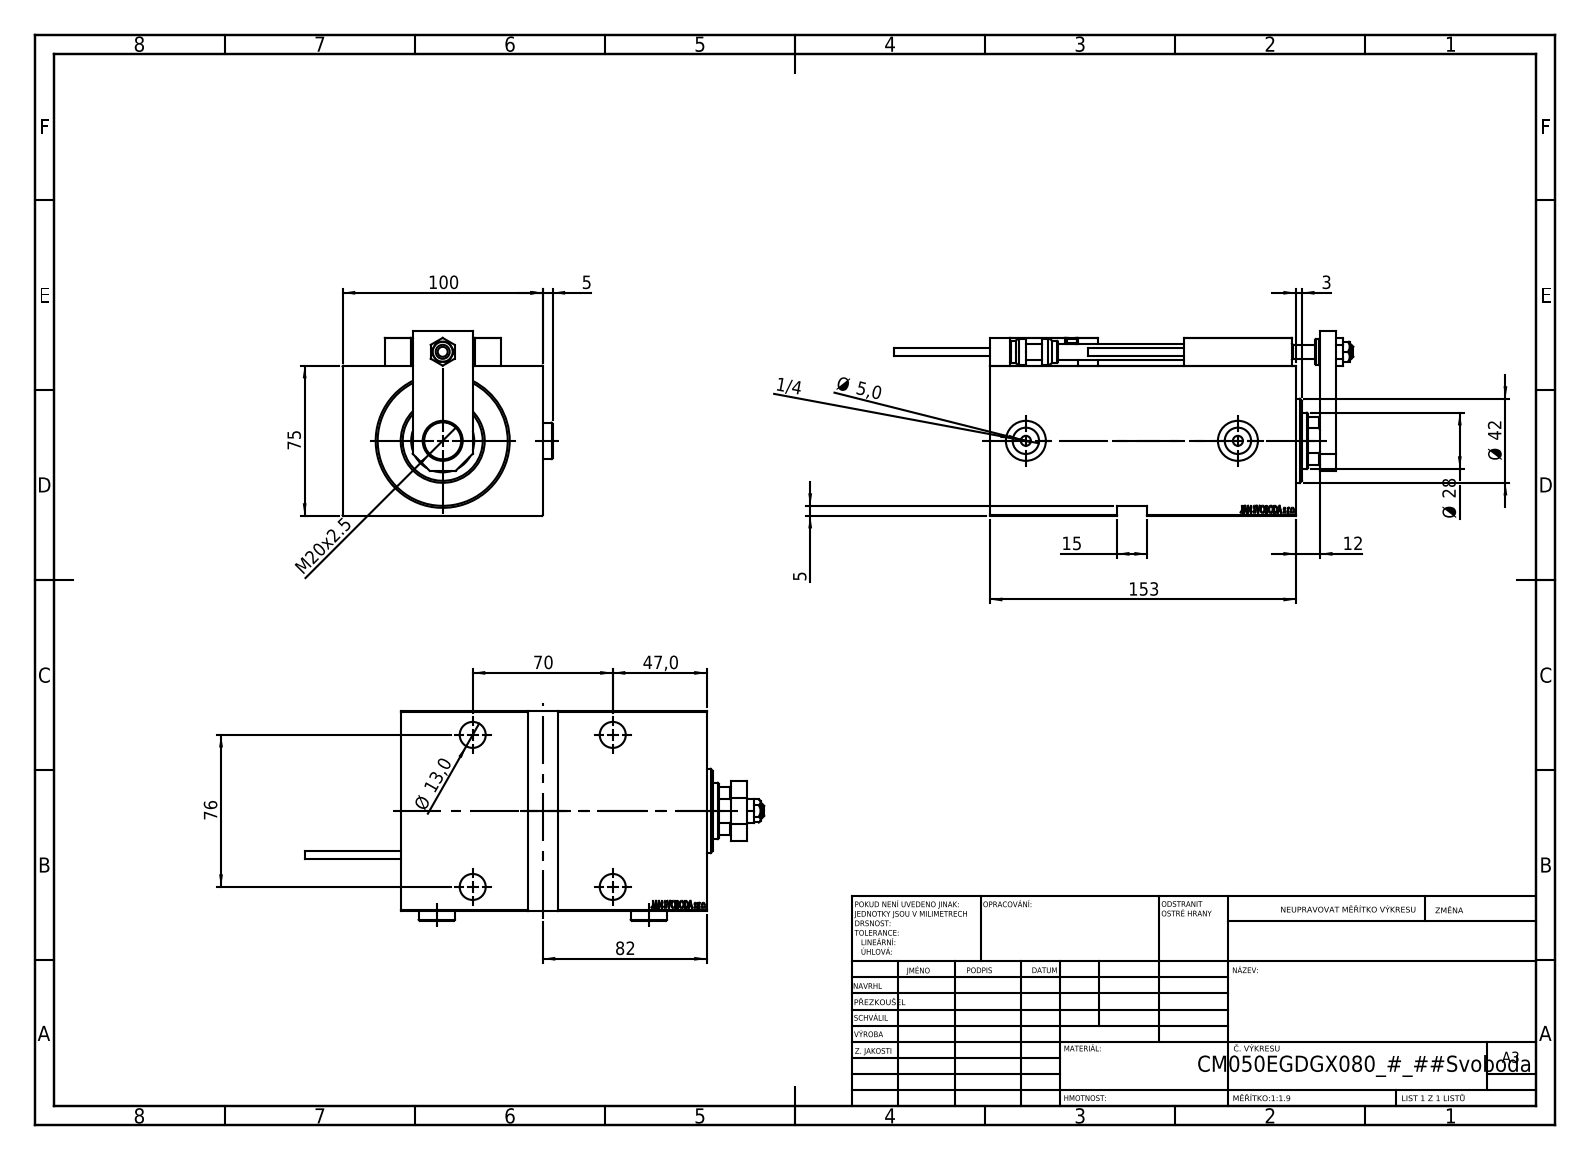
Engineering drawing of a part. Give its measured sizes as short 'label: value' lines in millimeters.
name: V450CM_E_Body; SWITCH DIM B,W; SWITCH_X_FRONT_BACK; V450CM_E_VCP (+7 more)
written by: SolidWorks 2019 (CONFIG_CONTROL_DESIGN)
unit: mm
bodies: 26 solids, 1349 faces (606 planar, 198 cylindrical, 545 other)
size: 229.7 × 104.9 × 92.5
volume: 1 041 000 mm³; area: 169 237 mm²
holes: 5× ⌀8, 4× ⌀3.2, 4× ⌀4, 4× ⌀5, 4× ⌀13, 4× ⌀19, 3× ⌀20, 2× ⌀13.16, 1× ⌀7, 1× ⌀18.5, 1× ⌀28, 1× ⌀31.5
bosses: 2× ⌀18, 2× ⌀5, 2× ⌀3.8, 1× ⌀52, 1× ⌀42, 1× ⌀13, 1× ⌀11
rounds: 30× R0.3, 2× R3, 1× R13.5
face distances: 75, 100, 14, 153, 5, 139, 25, 12, 8, 20
hole spacings: 11.37, 20, 29.59, 29.69, 36.06, 41.77, 42.19, 48.83
